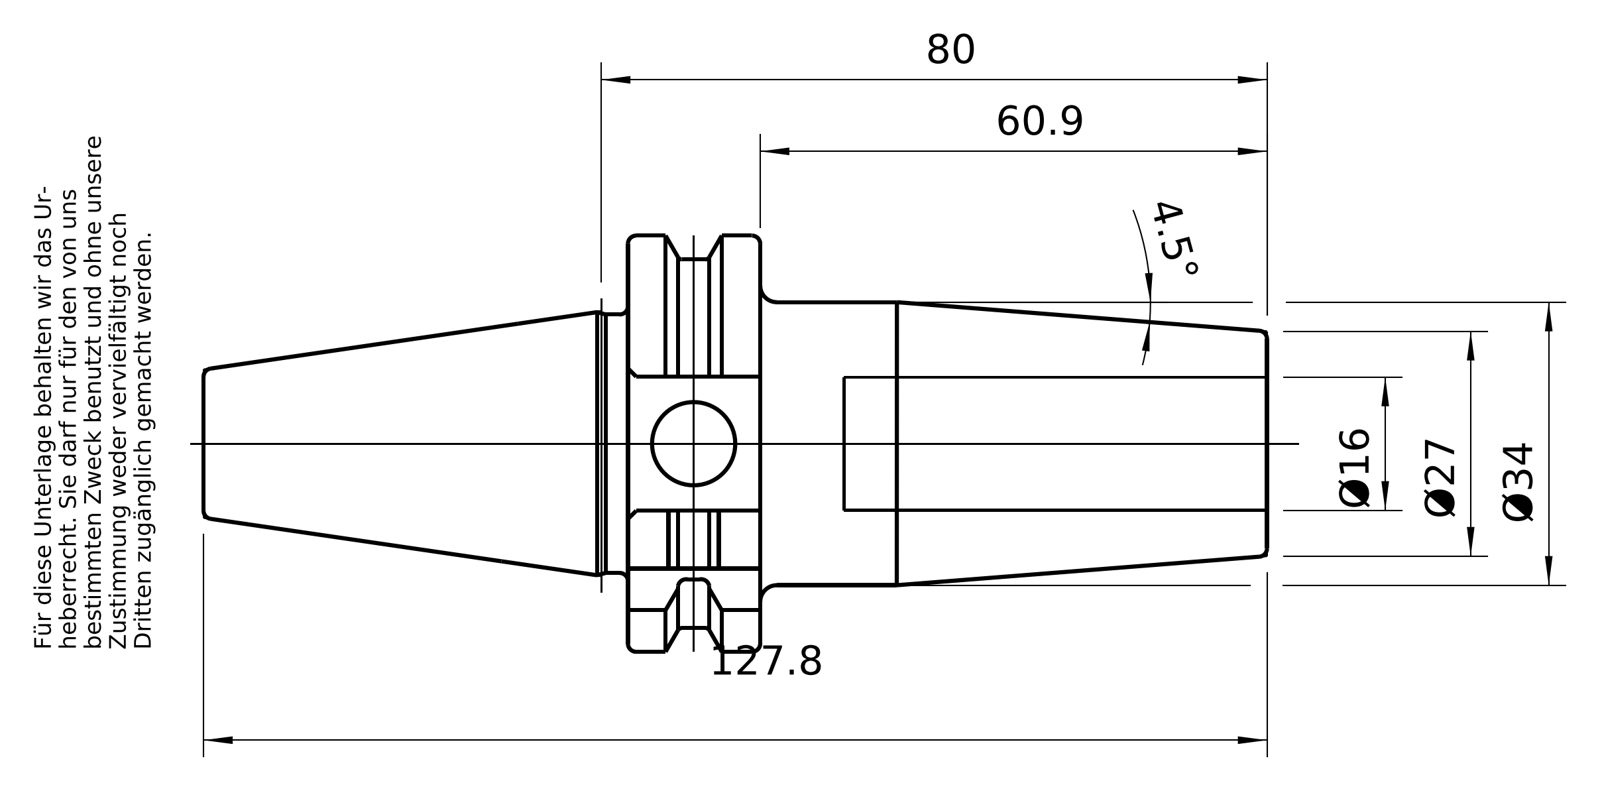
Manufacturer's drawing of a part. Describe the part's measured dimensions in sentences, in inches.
The part is named "30-440-16". Its 3-D file was written by "PRO/ENGINEER BY PARAMETRIC TECHNOLOGY CORPORATION, 2010430 (CONFIG_CONTROL_DESIGN)". It is 1 solid with 93 faces: 23 planar, 23 cylindrical and 47 other. Overall it measures 5.026 by 1.968 by 1.863 inches. Its volume is 5.249 cubic inches and its surface area 31 square inches. Round holes: 1 of diameter 0.398, 1 of diameter 0.512, 1 of diameter 0.531, 1 of diameter 0.63. Round bosses or shafts: 1 of diameter 1.339, 1 of diameter 1.222, 1 of diameter 0.473. Partial cylindrical surfaces (rounded edges, fillets, slot ends): 1 of radius 0.867, 1 of radius 0.984. The main face-to-face distances are 0.624, 2.4, 3.024, 1.382, 1.055, 0.431, 1.969, 0.634, 0.274, 0.907.
